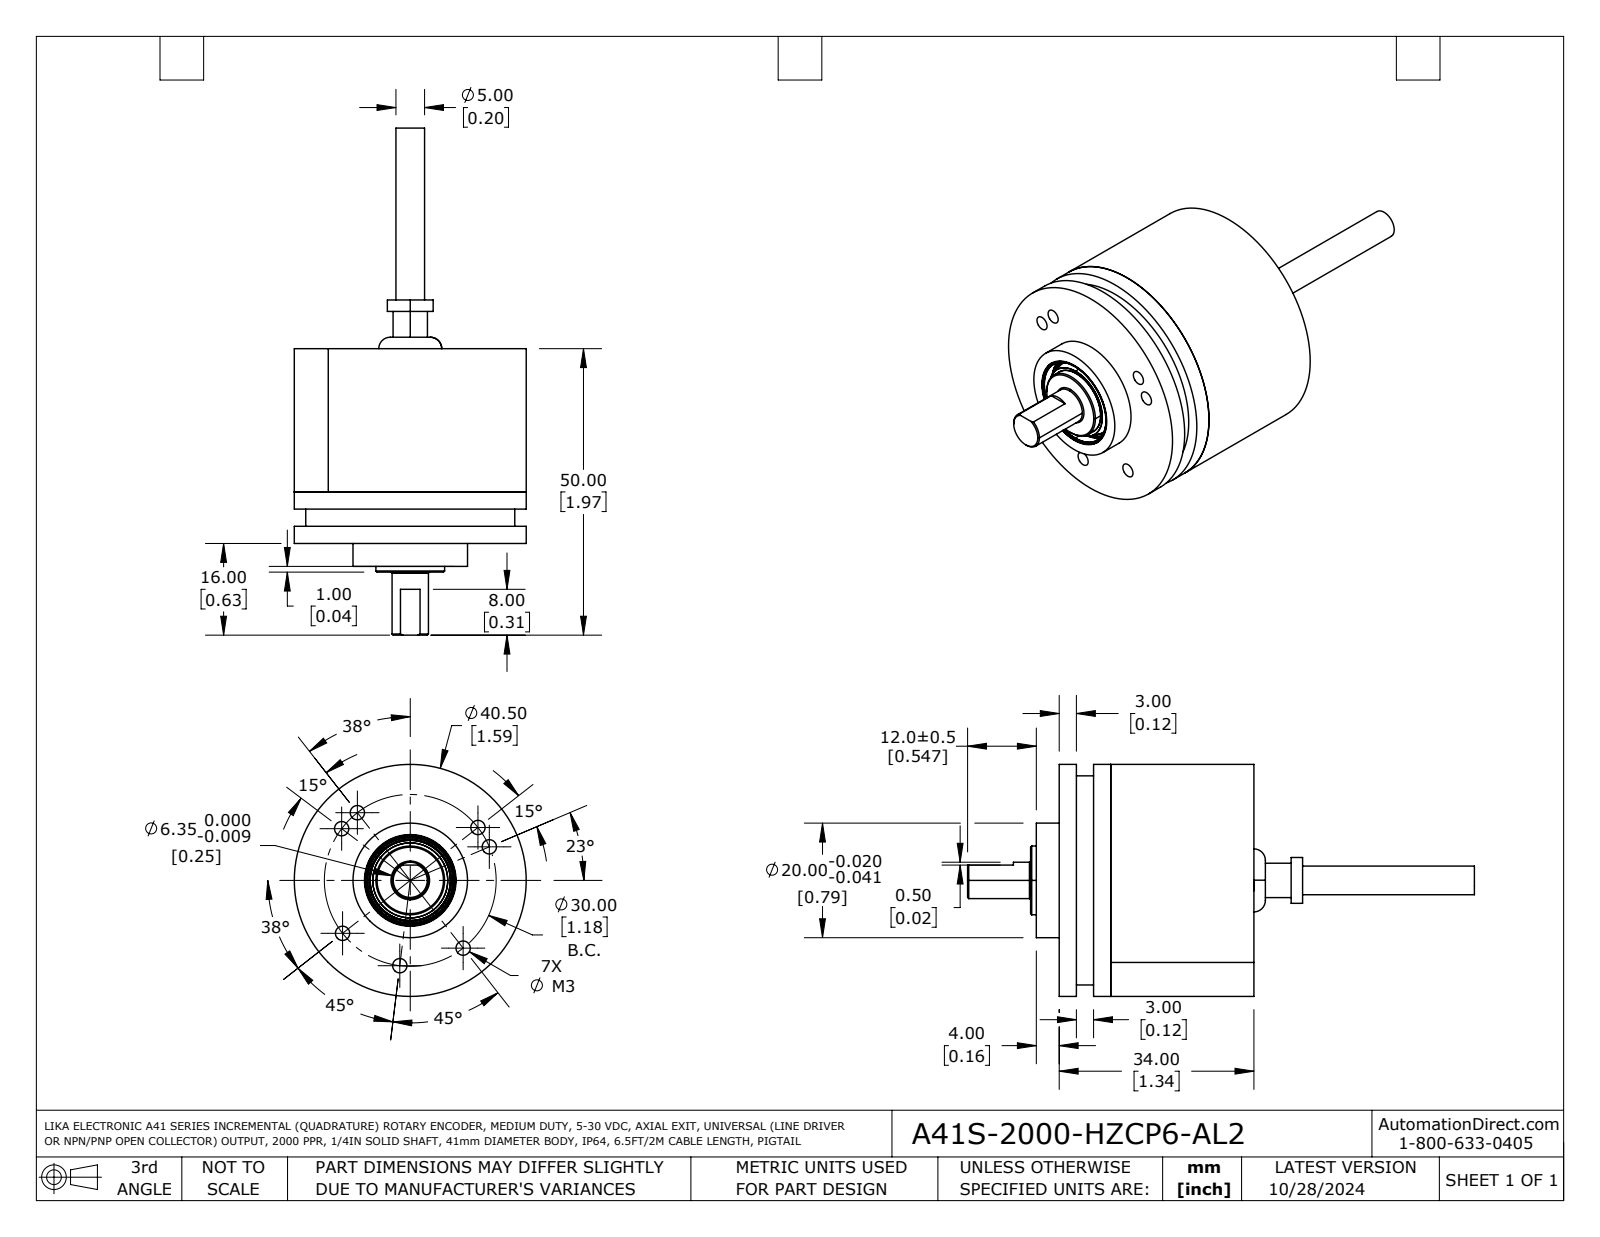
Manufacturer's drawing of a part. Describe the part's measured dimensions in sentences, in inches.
The part is named "A41S-2000-HZCP6-AL2". Its 3-D file was written by "SolidWorks 2021 (AUTOMOTIVE_DESIGN)". It is 11 solids with 422 faces: 76 planar, 145 cylindrical and 201 other. Overall it measures 3.484 by 1.594 by 1.594 inches. Its volume is 1.175 cubic inches and its surface area 28.29 square inches. Round holes: 7 of diameter 0.063, 7 of diameter 0.098, 3 of diameter 0.157, 2 of diameter 0.087, 1 of diameter 0.169, 1 of diameter 0.295, 1 of diameter 0.512, 1 of diameter 0.602, 1 of diameter 0.612, 1 of diameter 0.63, 1 of diameter 1.516. Round bosses or shafts: 2 of diameter 0.079, 1 of diameter 1.594, 1 of diameter 1.496, 1 of diameter 1.457, 1 of diameter 1.437, 1 of diameter 0.787, 1 of diameter 0.472, 1 of diameter 0.315. Partial cylindrical surfaces (rounded edges, fillets, slot ends): 14 of radius 0.039, 6 of radius 0.007, 2 of radius 0.008. The main face-to-face distances are 0.118, 1.339, 0.433, 0.906, 1.22, 0.079, 0.866, 0.984, 0.787, 0.039. The hole center spacings are 0.591, 0.669, 0.835, 0.11, 0.118, 0.837, 0.945, 1.257.
